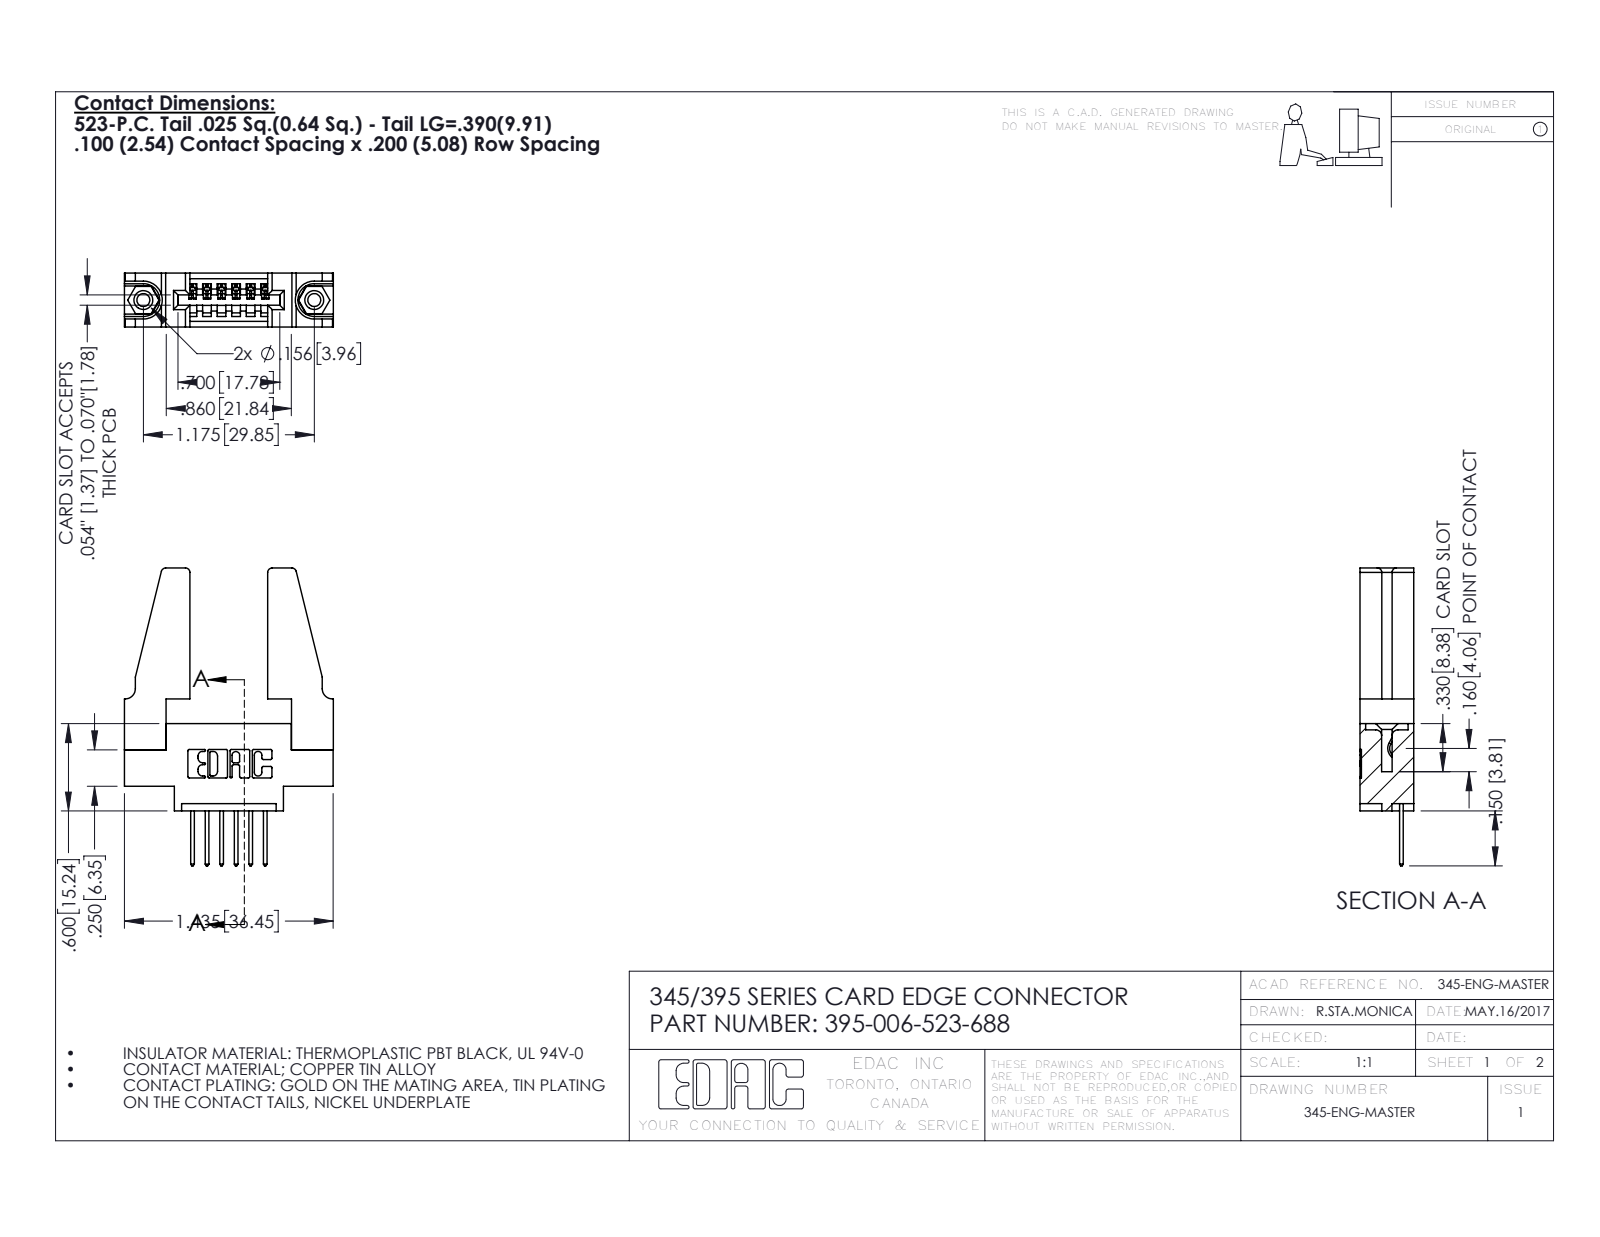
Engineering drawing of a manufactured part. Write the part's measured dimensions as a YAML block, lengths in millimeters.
part_name: "345-292-001_345-293-123; 345-220-078_345-220-088; 345-250-001_345-250-001-102; 395-006-523-688 (+1 more)"
step_written_by: "SolidWorks 2016 (CONFIG_CONTROL_DESIGN)"
units: millimeters
bodies: {solids: 11, faces: 602, planar: 396, cylindrical: 190, other: 16}
overall_size: [52, 36.5, 9.4]
volume: 6310
surface_area: 6832
round_holes:
  - {diameter: 2.3, count: 2}
  - {diameter: 3.2, count: 2}
  - {diameter: 4, count: 2}
  - {diameter: 1.6, count: 1}
round_bosses_or_shafts:
  - {diameter: 3.9, count: 2}
partial_cylinders:
  - {radius: 0.3, count: 22}
  - {radius: 0.2, count: 12}
  - {radius: 0.3, count: 12}
  - {radius: 0.8, count: 8}
  - {radius: 0.2, count: 6}
  - {radius: 0.8, count: 6}
  - {radius: 0.7, count: 3}
  - {radius: 0.8, count: 2}
face_to_face_distances: [9.4, 1.8, 7.6, 5.1, 3.8, 3.8, 2.5, 6.9, 0.6, 5.6]
hole_center_spacings: [6.9, 24, 29.8]
